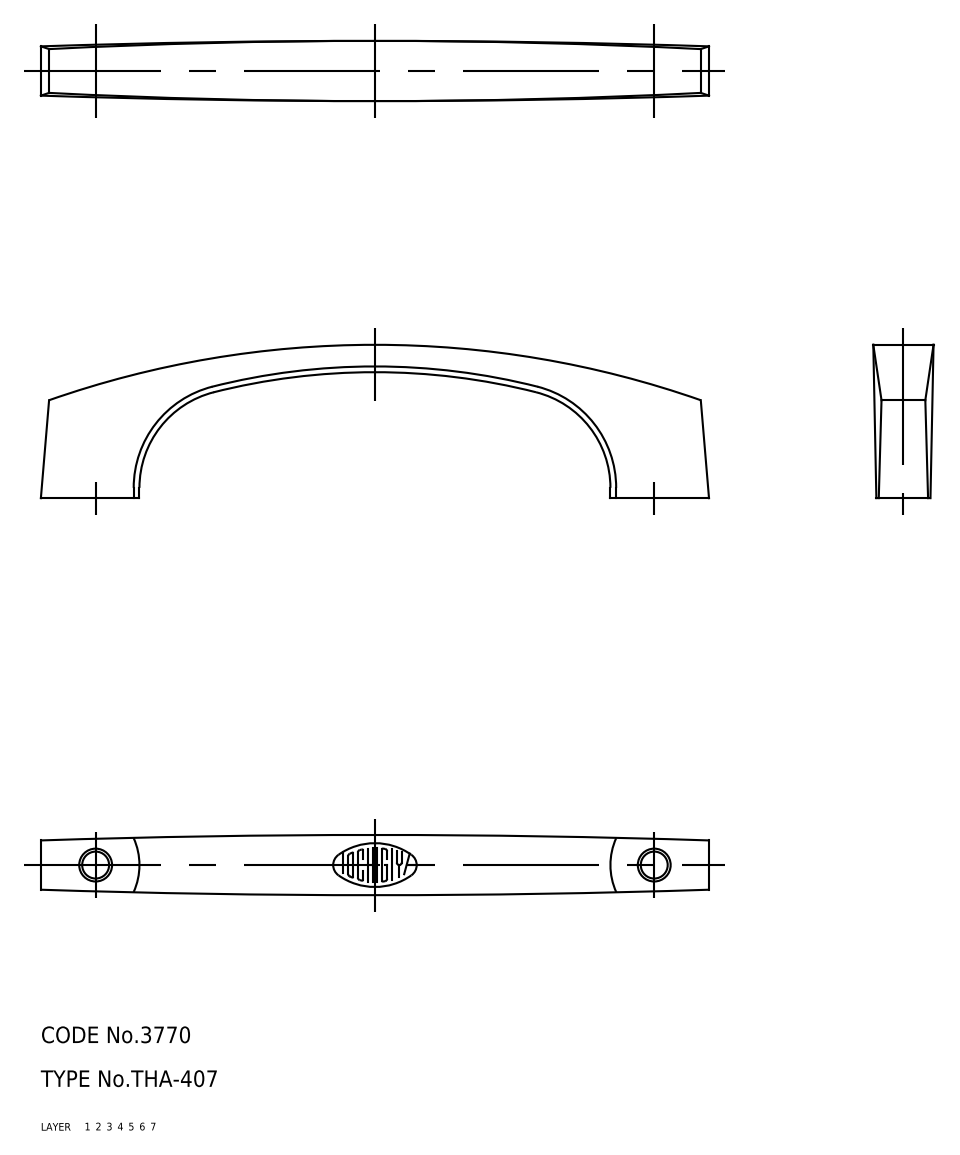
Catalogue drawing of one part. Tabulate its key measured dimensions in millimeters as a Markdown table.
| quantity | value |
| --- | --- |
| part name | pull |
| STEP written by | CADfix (AUTOMOTIVE_DESIGN) |
| units | millimeters |
| bodies | 1 solid, 18 faces (0 planar, 0 cylindrical, 18 other) |
| overall size | 122 × 28 × 11.01 |
| volume | 11 391 mm³ |
| surface area | 5 714 mm² |
